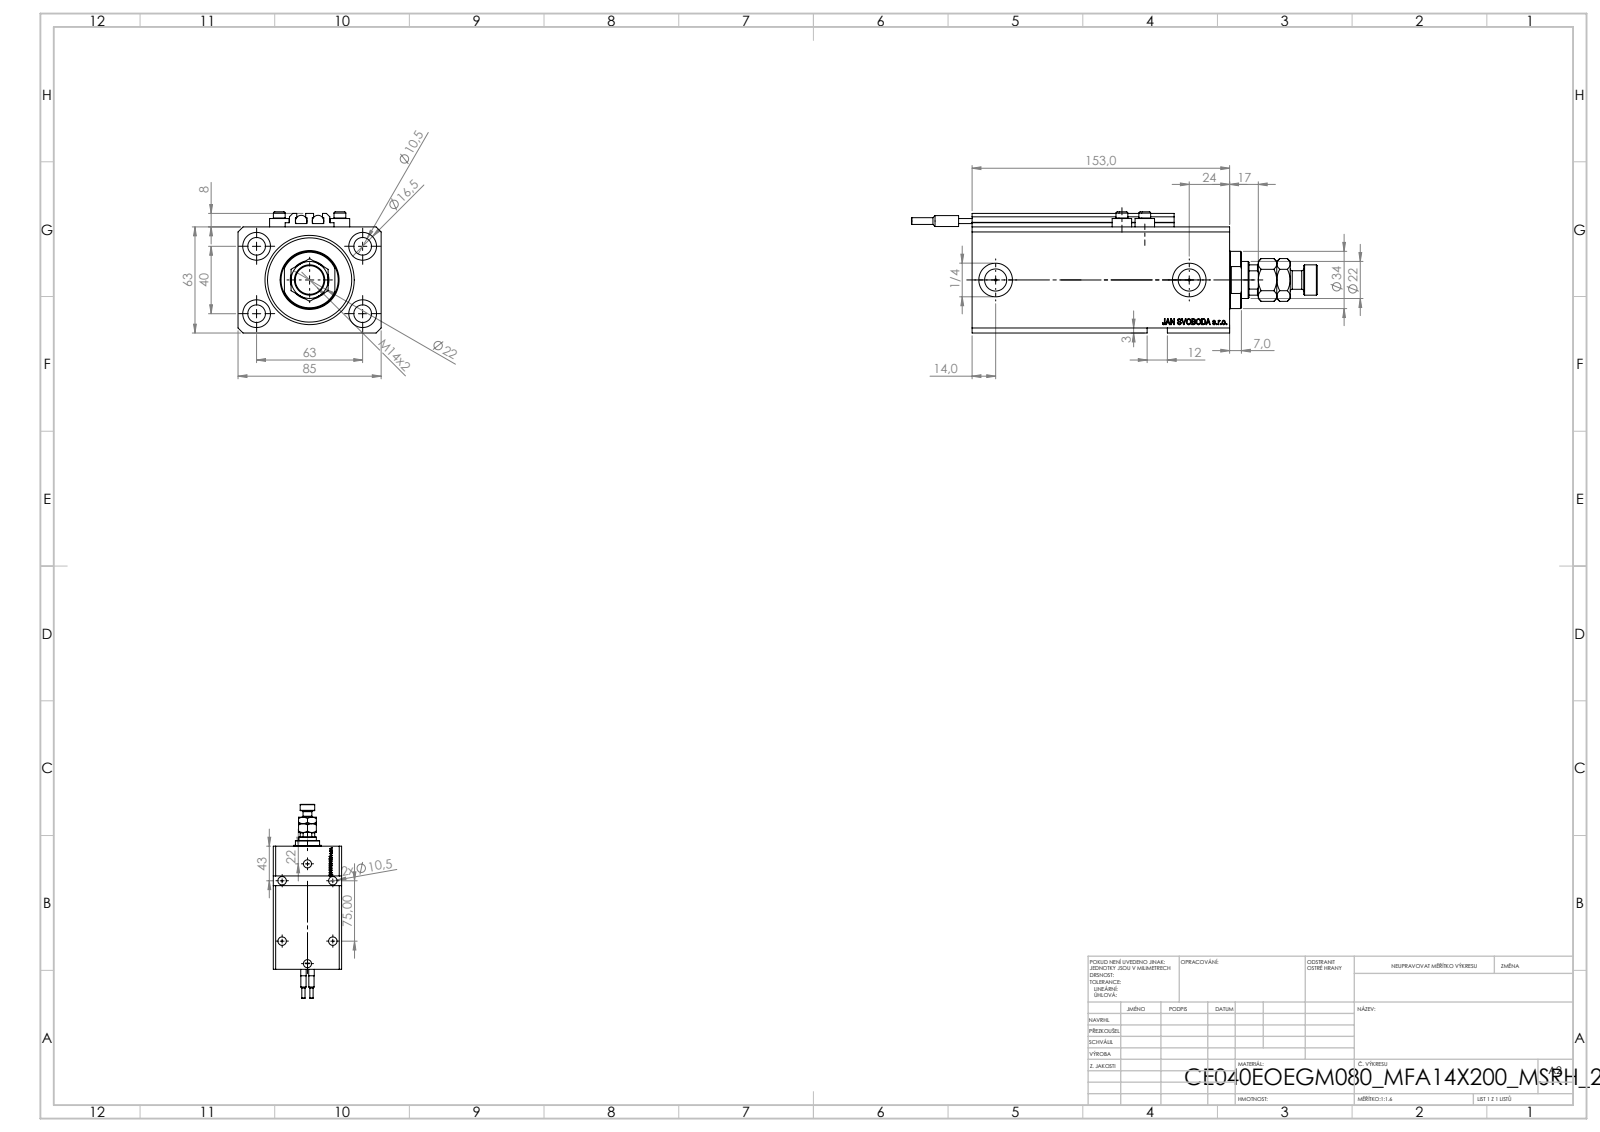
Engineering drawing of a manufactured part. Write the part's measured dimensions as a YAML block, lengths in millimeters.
part_name: "MFA; V250CE_VC_E; V250CE_E_Body; V250CE_C_VCP (+2 more)"
step_written_by: "SolidWorks 2019 (CONFIG_CONTROL_DESIGN)"
units: millimeters
bodies: {solids: 11, faces: 1211, planar: 583, cylindrical: 162, other: 466}
overall_size: [241, 85, 72]
volume: 698110
surface_area: 146803
round_holes:
  - {diameter: 10.5, count: 8}
  - {diameter: 1.25, count: 4}
  - {diameter: 4, count: 4}
  - {diameter: 16.5, count: 4}
  - {diameter: 10, count: 2}
  - {diameter: 13.16, count: 2}
  - {diameter: 20, count: 2}
  - {diameter: 12.5, count: 1}
  - {diameter: 22, count: 1}
  - {diameter: 40, count: 1}
  - {diameter: 53, count: 1}
round_bosses_or_shafts:
  - {diameter: 11.6, count: 4}
  - {diameter: 7, count: 4}
  - {diameter: 6.8, count: 2}
  - {diameter: 6.5, count: 2}
  - {diameter: 4, count: 2}
  - {diameter: 34, count: 1}
  - {diameter: 18, count: 1}
  - {diameter: 11, count: 1}
partial_cylinders:
  - {radius: 0.2, count: 10}
  - {radius: 10.5, count: 1}
face_to_face_distances: [63, 85, 17, 153, 136, 65, 3, 11.4, 124.6, 141.6]
hole_center_spacings: [37.31, 63, 13.6, 15.4, 24.96, 33.62, 36, 37.86]
